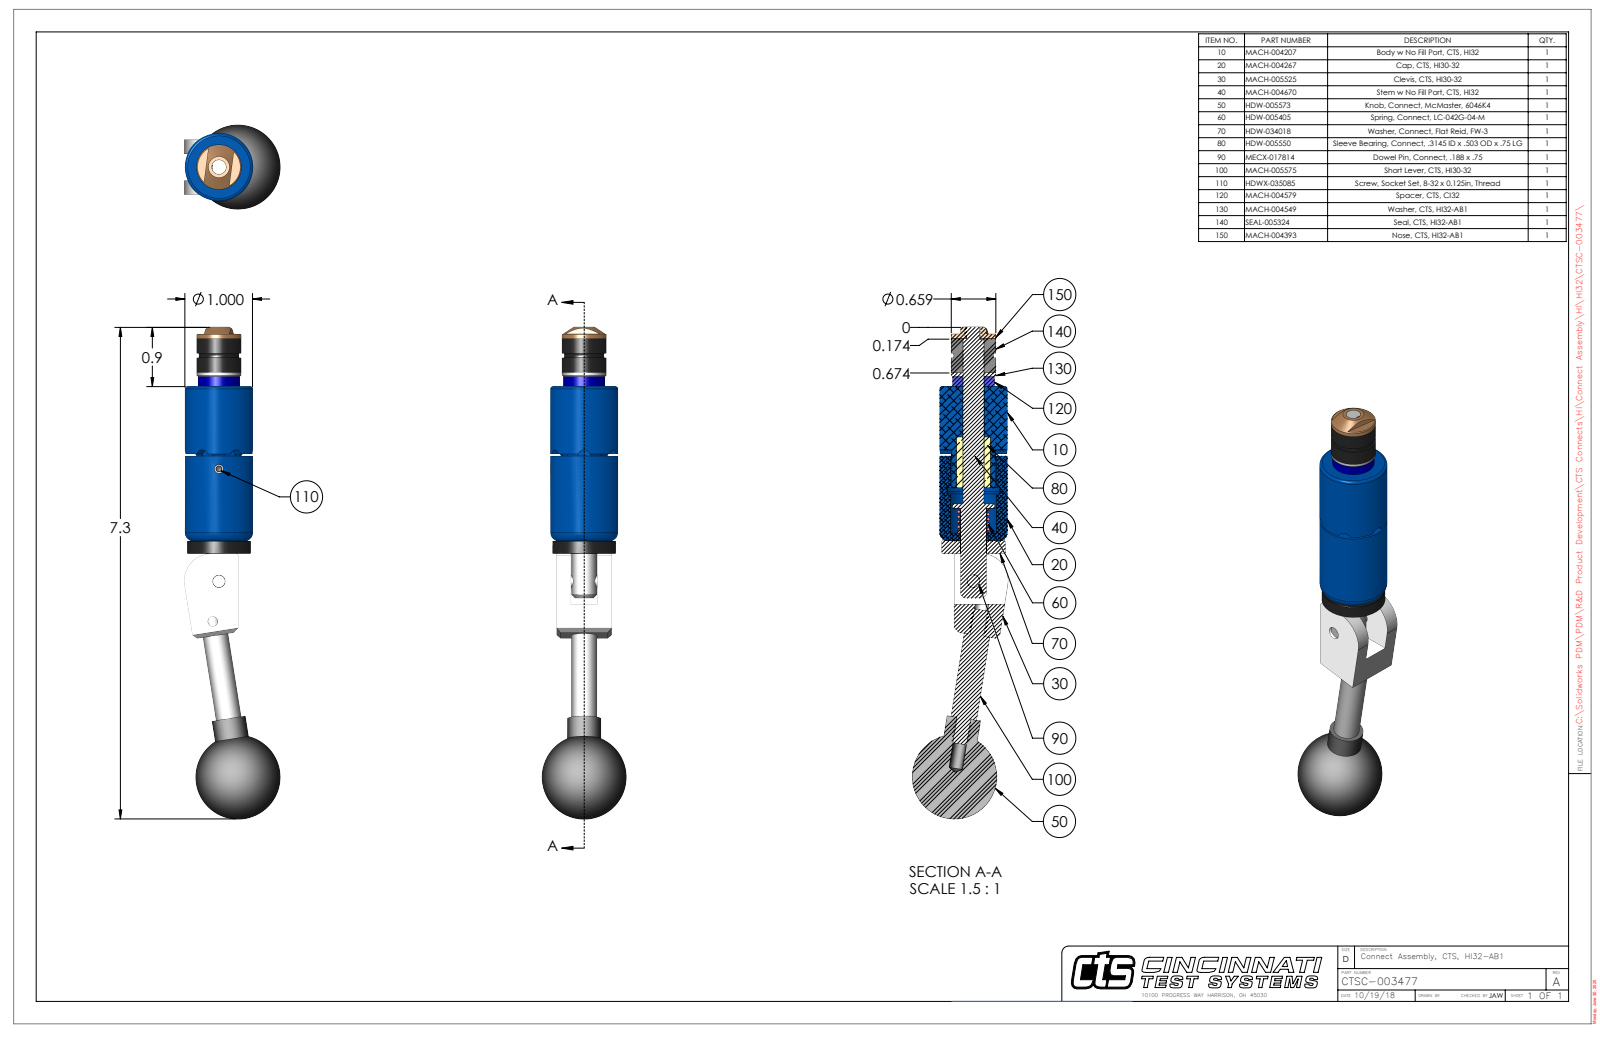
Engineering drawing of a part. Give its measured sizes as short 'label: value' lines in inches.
name: CTSC-003477
written by: SolidWorks 2023 (AUTOMOTIVE_DESIGN)
unit: in
bodies: 10 solids, 254 faces (97 planar, 100 cylindrical, 57 other)
size: 7.268 × 1.416 × 1.25
volume: 3.922 in³; area: 32.99 in²
holes: 2× ⌀0.201, 1× ⌀0.136, 1× ⌀0.15, 1× ⌀0.189, 1× ⌀0.213, 1× ⌀0.31, 1× ⌀0.314, 1× ⌀0.316, 1× ⌀0.385, 1× ⌀0.392
bosses: 2× ⌀0.25, 2× ⌀0.201, 1× ⌀1, 1× ⌀0.936, 1× ⌀0.659, 1× ⌀0.618, 1× ⌀0.5, 1× ⌀0.38
rounds: 6× R0.093, 2× R0.029, 1× R0.344, 1× R0.4, 1× R0.463
face distances: 0.21, 0.602, 2.283, 0.812, 2.47, 0.187, 0.702, 2.985, 3.172, 0.5
hole spacings: 0.599, 1.658, 2.252
